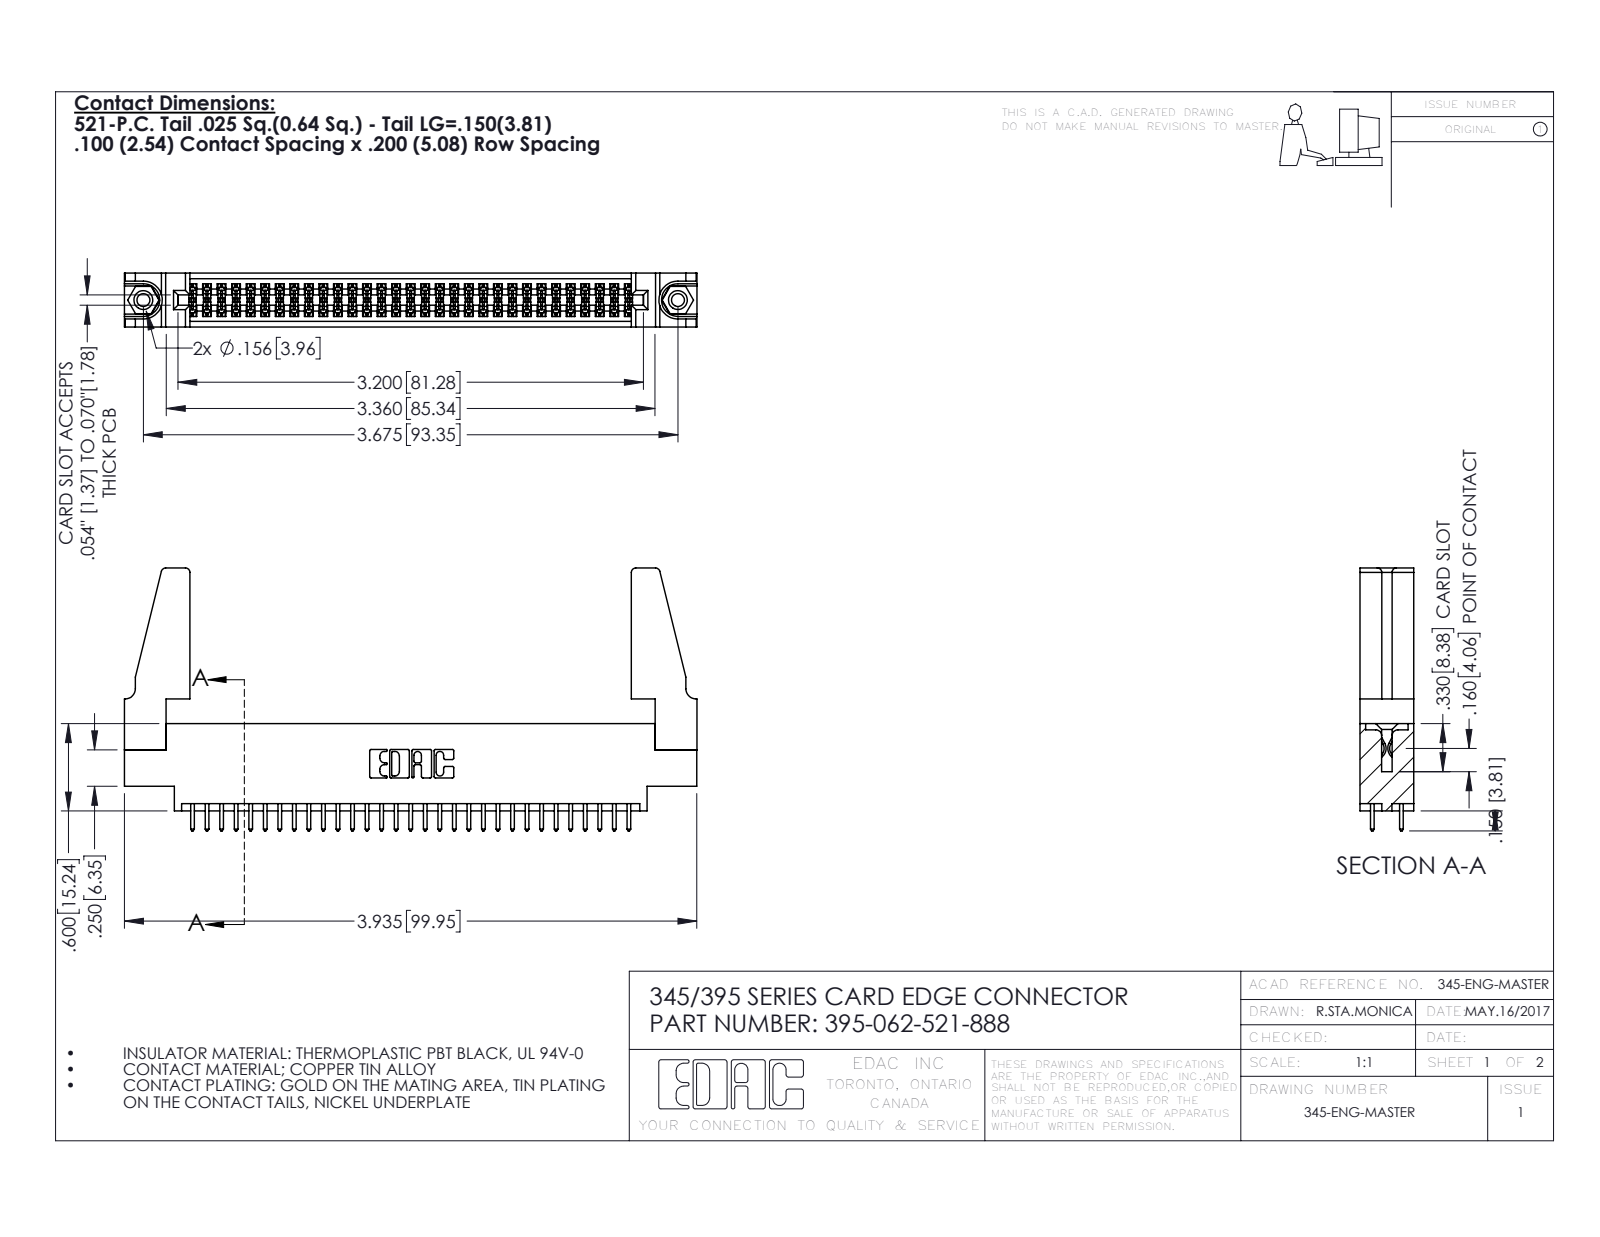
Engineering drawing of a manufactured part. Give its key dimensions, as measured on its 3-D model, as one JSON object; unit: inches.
{"part_name": "345-220-078_345-220-088; 395-062-521-888; 345 Part_0.170 Offset - 0.156 Dia-TH; 345-250-001_345-250-001-102 (+1 more)", "step_written_by": "SolidWorks 2016 (CONFIG_CONTROL_DESIGN)", "units": "inches", "bodies": {"solids": 67, "faces": 3354, "planar": 2202, "cylindrical": 1136, "other": 16}, "overall_size": [3.936, 1.807, 0.37], "volume_in3": 0.776, "surface_area_in2": 26.18, "round_holes": [[0.089, 2], [0.125, 2], [0.156, 2], [0.064, 1]], "round_bosses_or_shafts": [[0.155, 2]], "partial_cylinders_radius": [[0.006, 93], [0.01, 62], [0.01, 22], [0.03, 8], [0.007, 6], [0.031, 6], [0.026, 3], [0.014, 2]], "face_to_face_distances": [0.072, 0.298, 0.37, 0.2, 0.098, 0.272, 0.025, 0.225, 0.175, 0.149], "hole_center_spacings": [0.27, 3.44, 3.675]}
